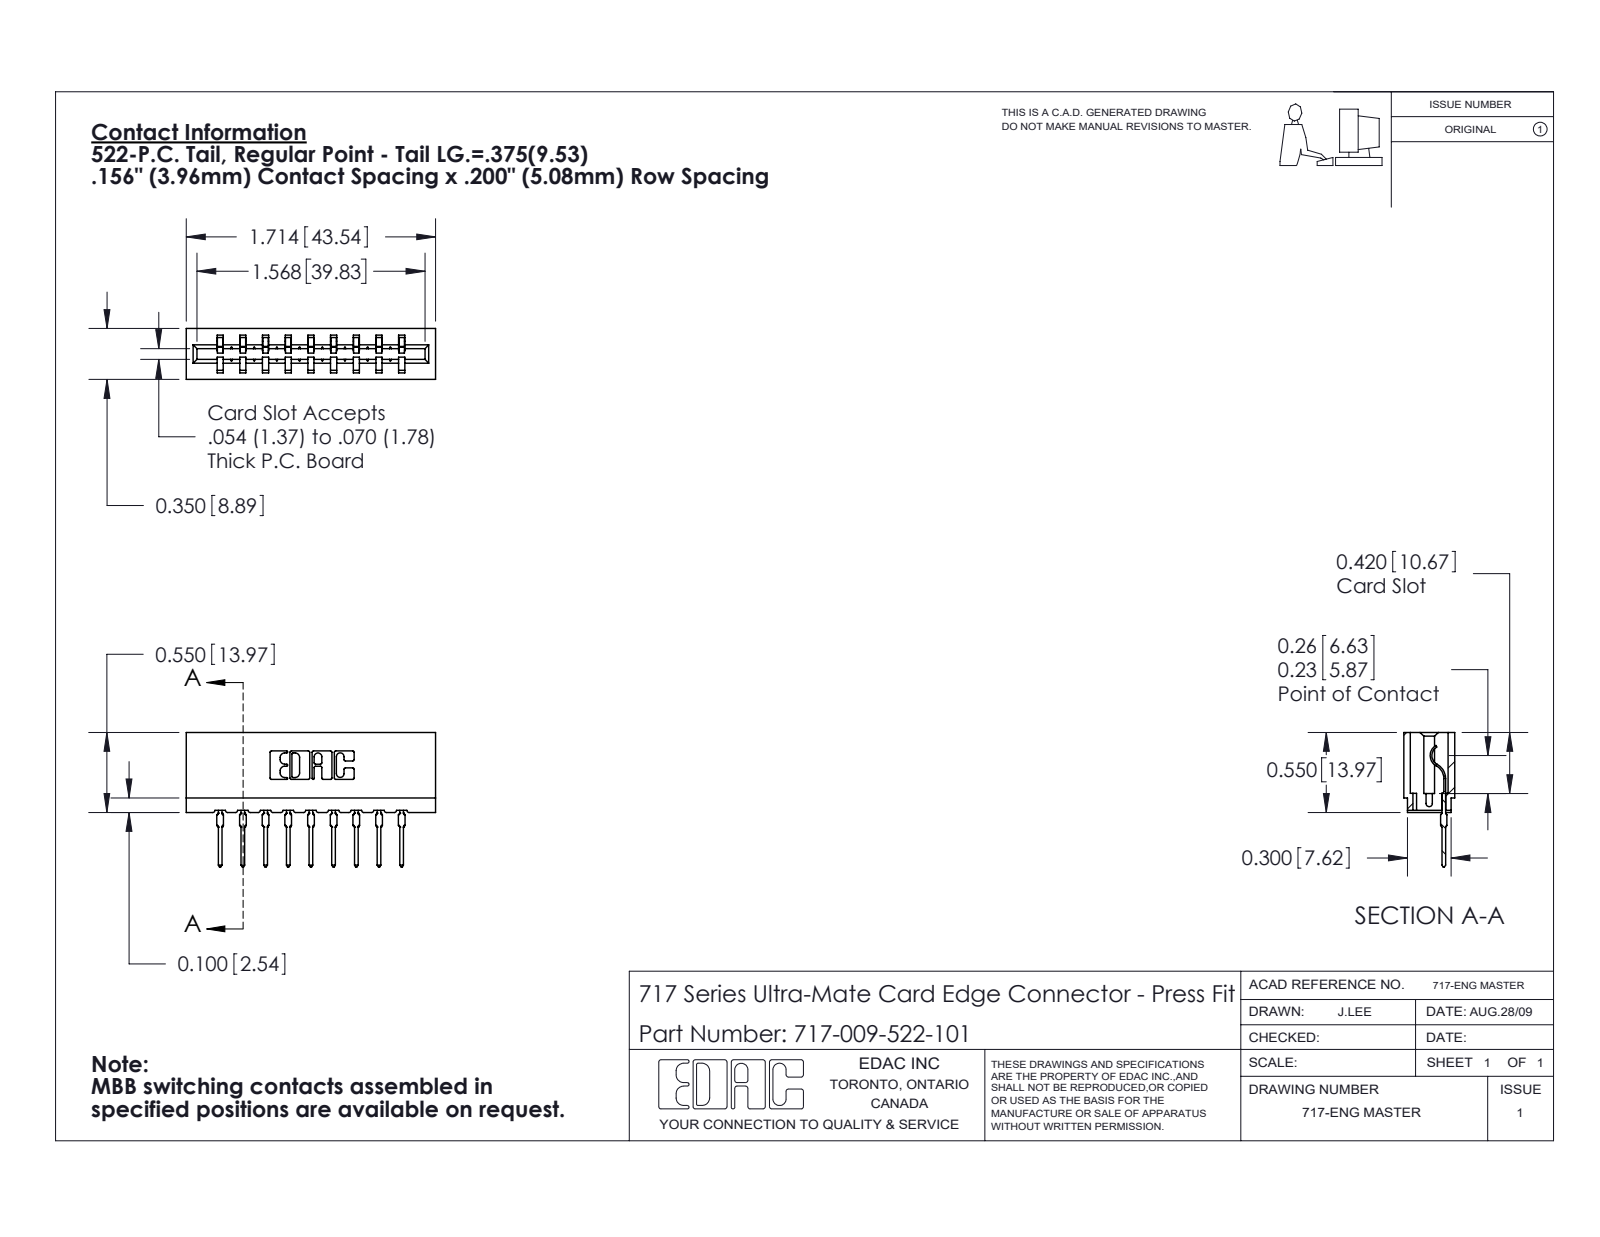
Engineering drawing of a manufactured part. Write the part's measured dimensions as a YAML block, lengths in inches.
part_name: "745-292-001_522; 717 Part_Insulator Option - 06; 717-009-522-101"
step_written_by: "SolidWorks 2020 (CONFIG_CONTROL_DESIGN)"
units: inches
bodies: {solids: 10, faces: 1111, planar: 666, cylindrical: 211, other: 234}
overall_size: [1.714, 0.924, 0.35]
volume: 0.234
surface_area: 7.814
partial_cylinders:
  - {radius: 0.01, count: 22}
  - {radius: 0.015, count: 18}
  - {radius: 0.021, count: 18}
  - {radius: 0.007, count: 6}
  - {radius: 0.031, count: 6}
  - {radius: 0.005, count: 4}
  - {radius: 0.011, count: 4}
  - {radius: 0.026, count: 3}
face_to_face_distances: [0.156, 0.212, 0.624, 0.138, 0.468, 0.198, 0.35, 0.312, 0.042, 0.312]
